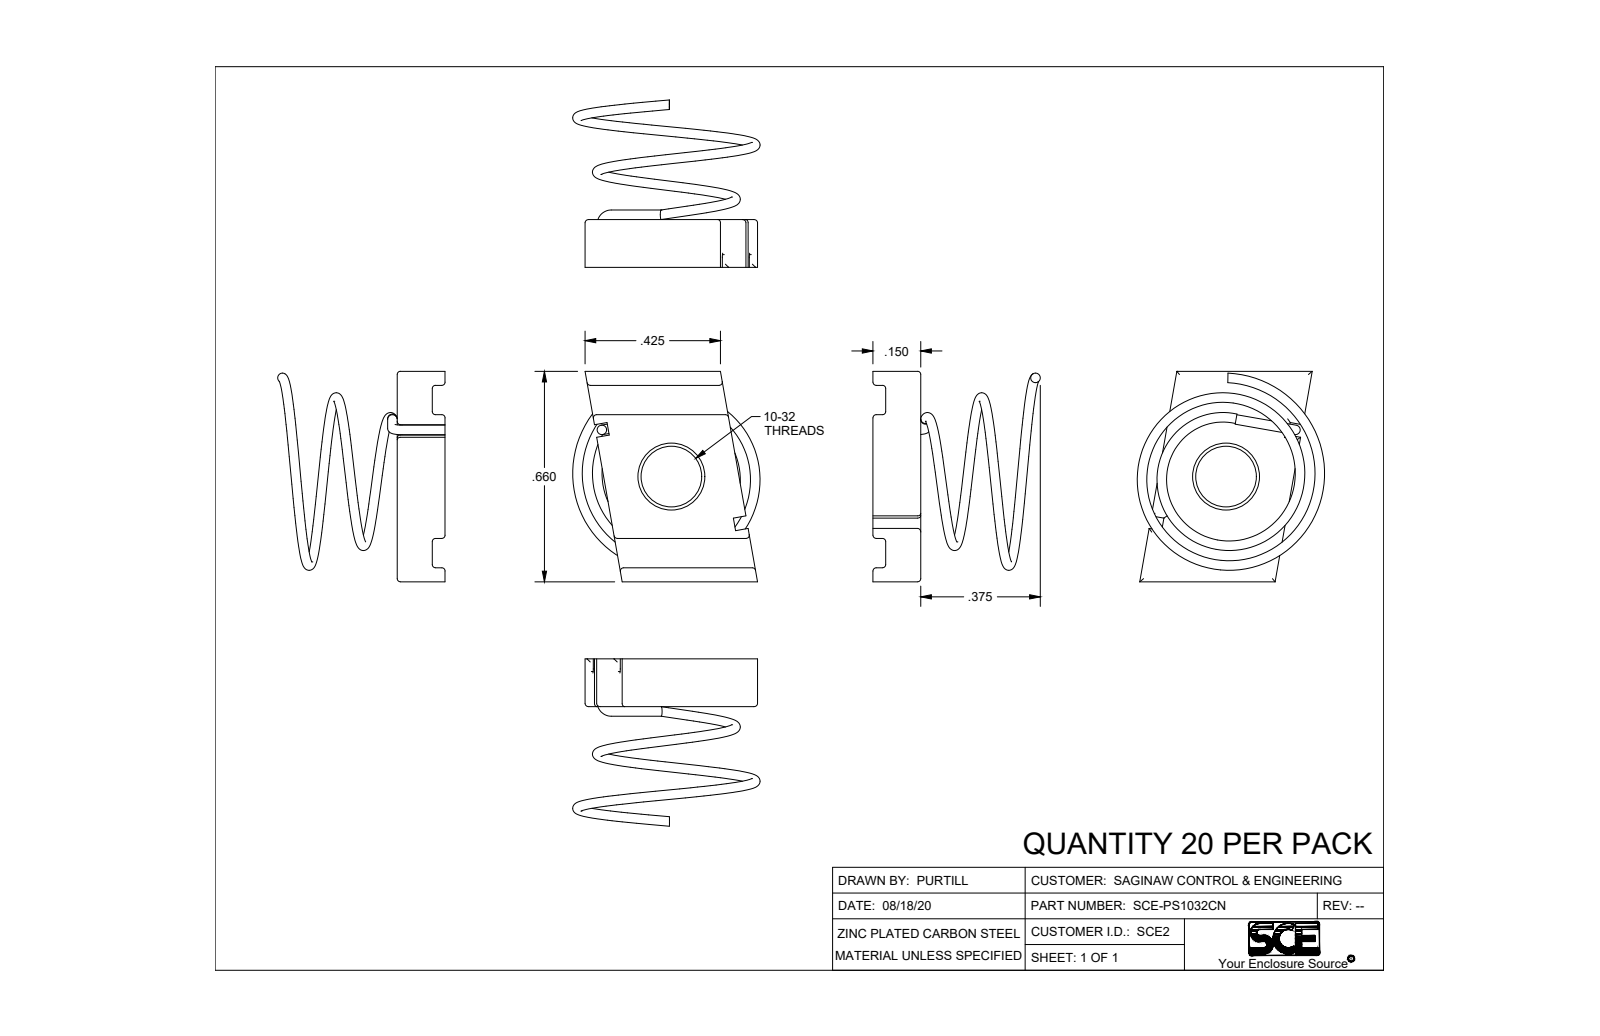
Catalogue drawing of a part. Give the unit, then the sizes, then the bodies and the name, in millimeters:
Units: millimetres
Overall size (bounding box): 16.8 × 14.9 × 13.3
Round holes (diameter × count): ⌀4.8 ×1
Round bosses / shafts (diameter × count): ⌀0.8 ×2
Partial cylindrical surfaces — rounded edges, fillets, slot ends (radius × count): R0.3 ×28
Main face-to-face distances: 3.8, 10.6, 1, 16.8, 2.8, 1.1, 15.6, 3.5, 13.3, 2.3
Volume: 610 mm³ · Surface area: 832 mm²
Bodies: 2 solids, 80 faces (26 planar, 38 cylindrical, 16 other)
Part name (STEP PRODUCT): SCE-PS1032CN
STEP written by: SolidWorks 2019 (CONFIG_CONTROL_DESIGN)
